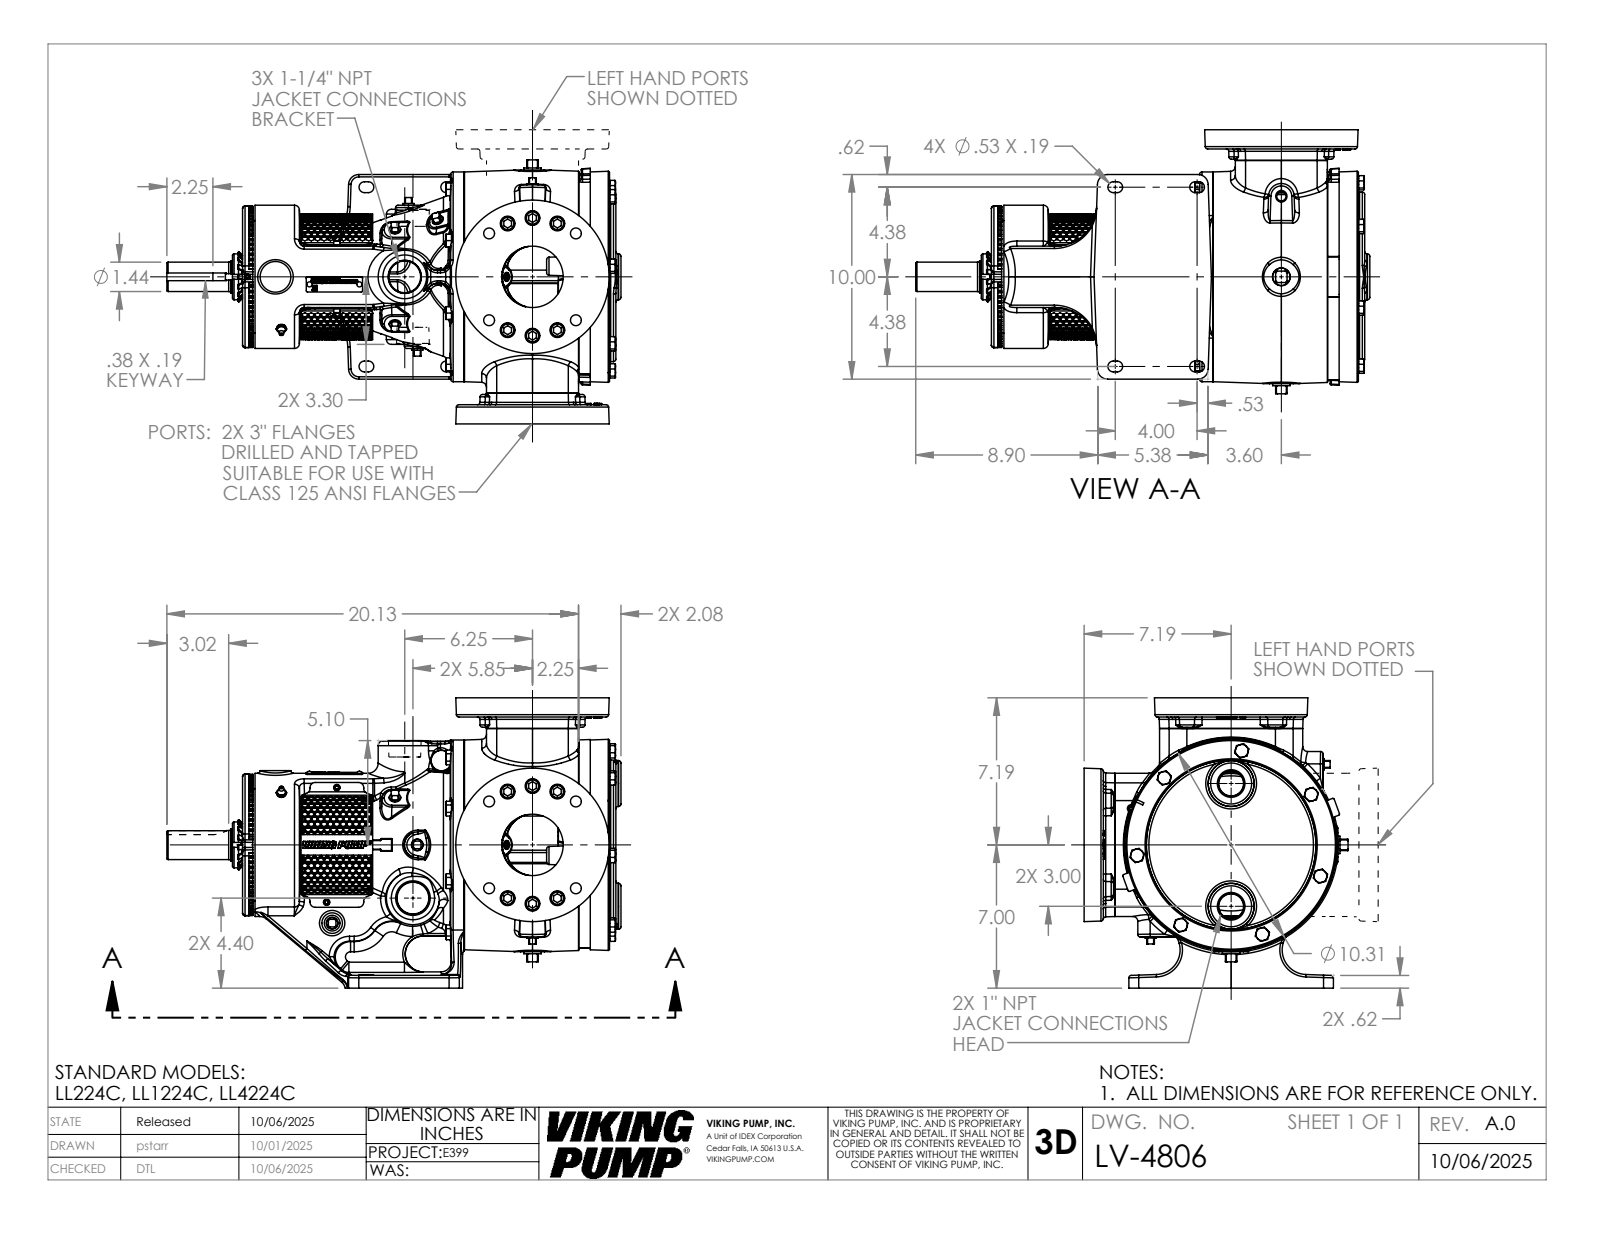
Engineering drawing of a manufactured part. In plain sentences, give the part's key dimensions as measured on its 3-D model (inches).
The part is named "LV-4806". Its 3-D file was written by "SolidWorks 2024 (AUTOMOTIVE_DESIGN)". It is 1 solid with 4998 faces: 1503 planar, 924 cylindrical and 2571 other. Overall it measures 22.2 by 14.188 by 12.903 inches. Its volume is 1 171 cubic inches and its surface area 1 400 square inches. Round holes: 12 of diameter 0.719, 9 of diameter 0.25, 8 of diameter 0.531, 8 of diameter 1.094, 6 of diameter 0.199, 3 of diameter 0.159, 2 of diameter 0.266, 2 of diameter 0.313, 2 of diameter 3, 1 of diameter 0.453, 1 of diameter 1.577, 1 of diameter 1.593. Round bosses or shafts: 12 of diameter 0.66, 8 of diameter 0.625, 7 of diameter 0.625, 3 of diameter 0.312, 3 of diameter 0.19, 1 of diameter 10.25, 1 of diameter 7, 1 of diameter 5.497. Partial cylindrical surfaces (rounded edges, fillets, slot ends): 109 of radius 0.063, 74 of radius 0.069, 66 of radius 0.01, 62 of radius 0.12, 26 of radius 0.5, 18 of radius 0.03, 17 of radius 0.06, 16 of radius 0.24. The main face-to-face distances are 14.187, 0.31, 2.25, 15.19, 15.5, 0.94, 2.75, 0.5, 3.54, 11.65. The hole center spacings are 3, 4.243, 2.875, 1.375, 1.028, 1.244, 2.18, 2.251.
